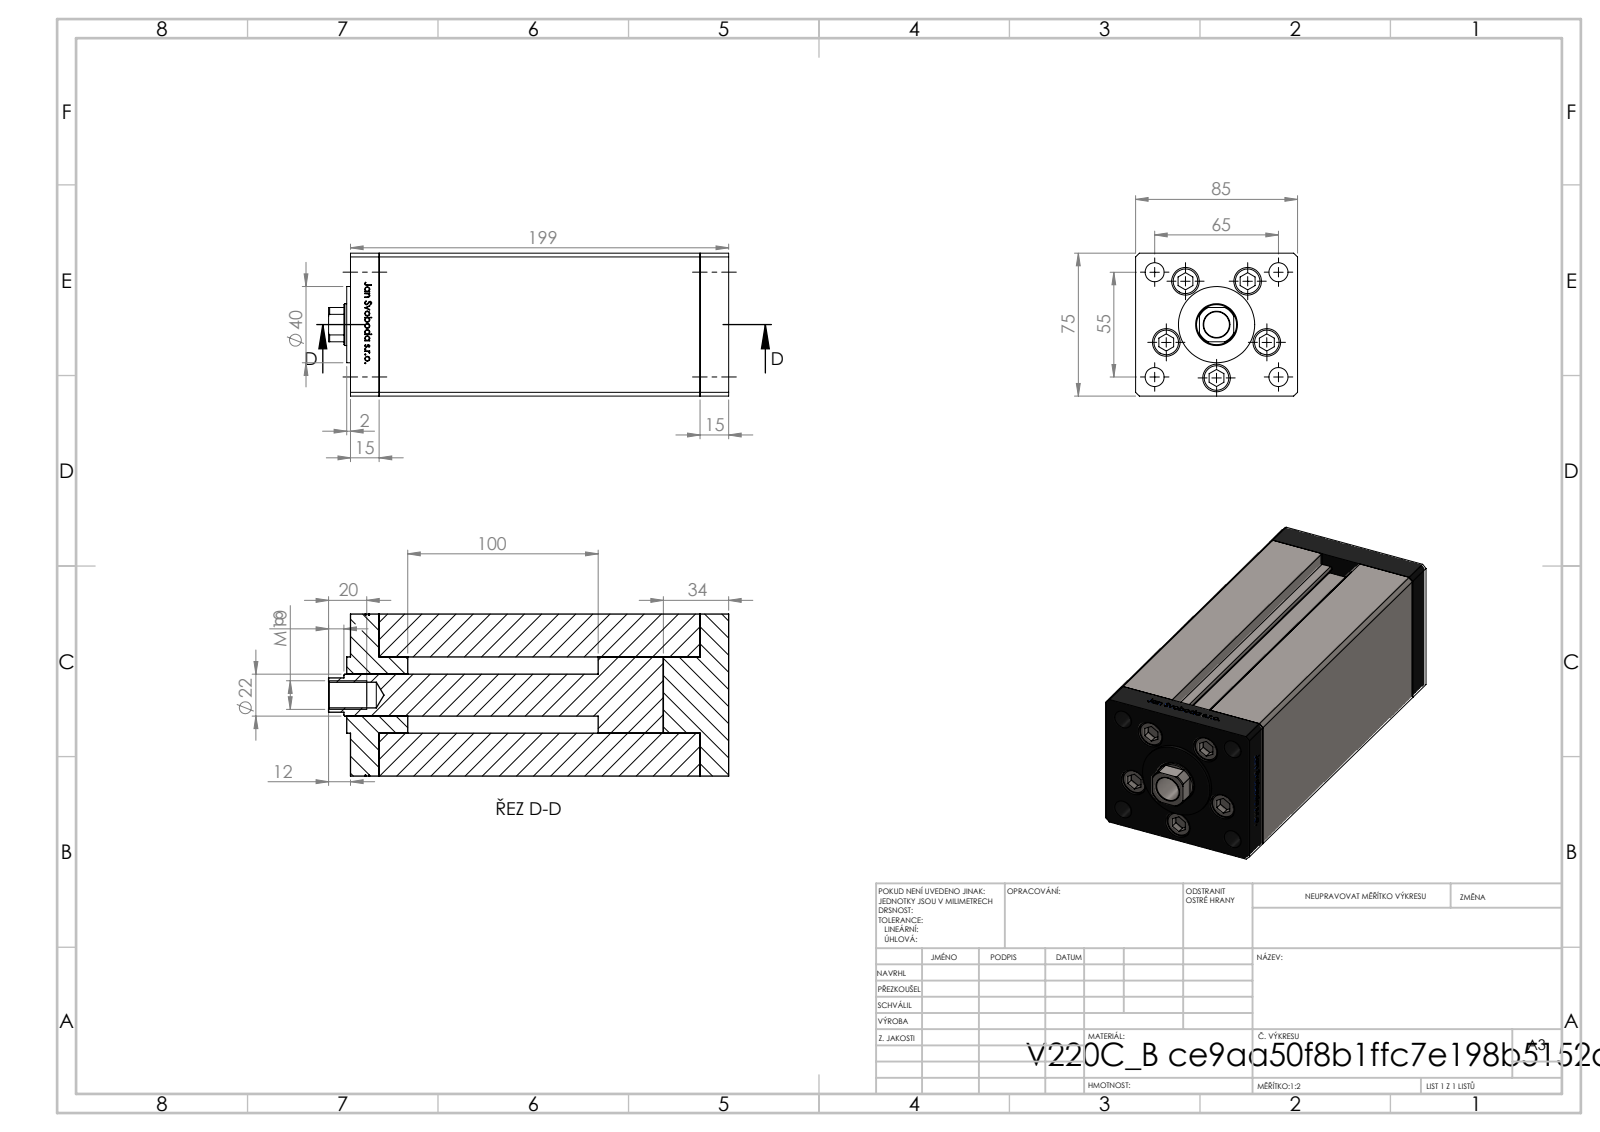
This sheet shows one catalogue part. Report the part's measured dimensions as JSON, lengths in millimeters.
{"part_name": "V220C_B MIDDLE; V220C BACK_B; V220C_FRONT_B; ALLEN BOLT (+1 more)", "step_written_by": "SolidWorks 2019 (CONFIG_CONTROL_DESIGN)", "units": "millimeters", "bodies": {"solids": 14, "faces": 1183, "planar": 462, "cylindrical": 147, "other": 574}, "overall_size": [210, 85, 75], "volume_mm3": 1118000, "surface_area_mm2": 171143, "round_holes": [[11, 5], [14.5, 5], [10, 4], [2, 2], [13.16, 2], [13.5, 1], [22, 1]], "round_bosses_or_shafts": [[8, 5], [40, 1]], "partial_cylinders_radius": [[0.93, 2], [10.5, 1]], "face_to_face_distances": [85, 75, 15, 168.5, 183.5, 198.5, 34.25, 68.5, 19.25, 149.25], "hole_center_spacings": [28, 42.57, 16.86, 19.17, 32.33, 32.5, 33.63, 37.33]}
